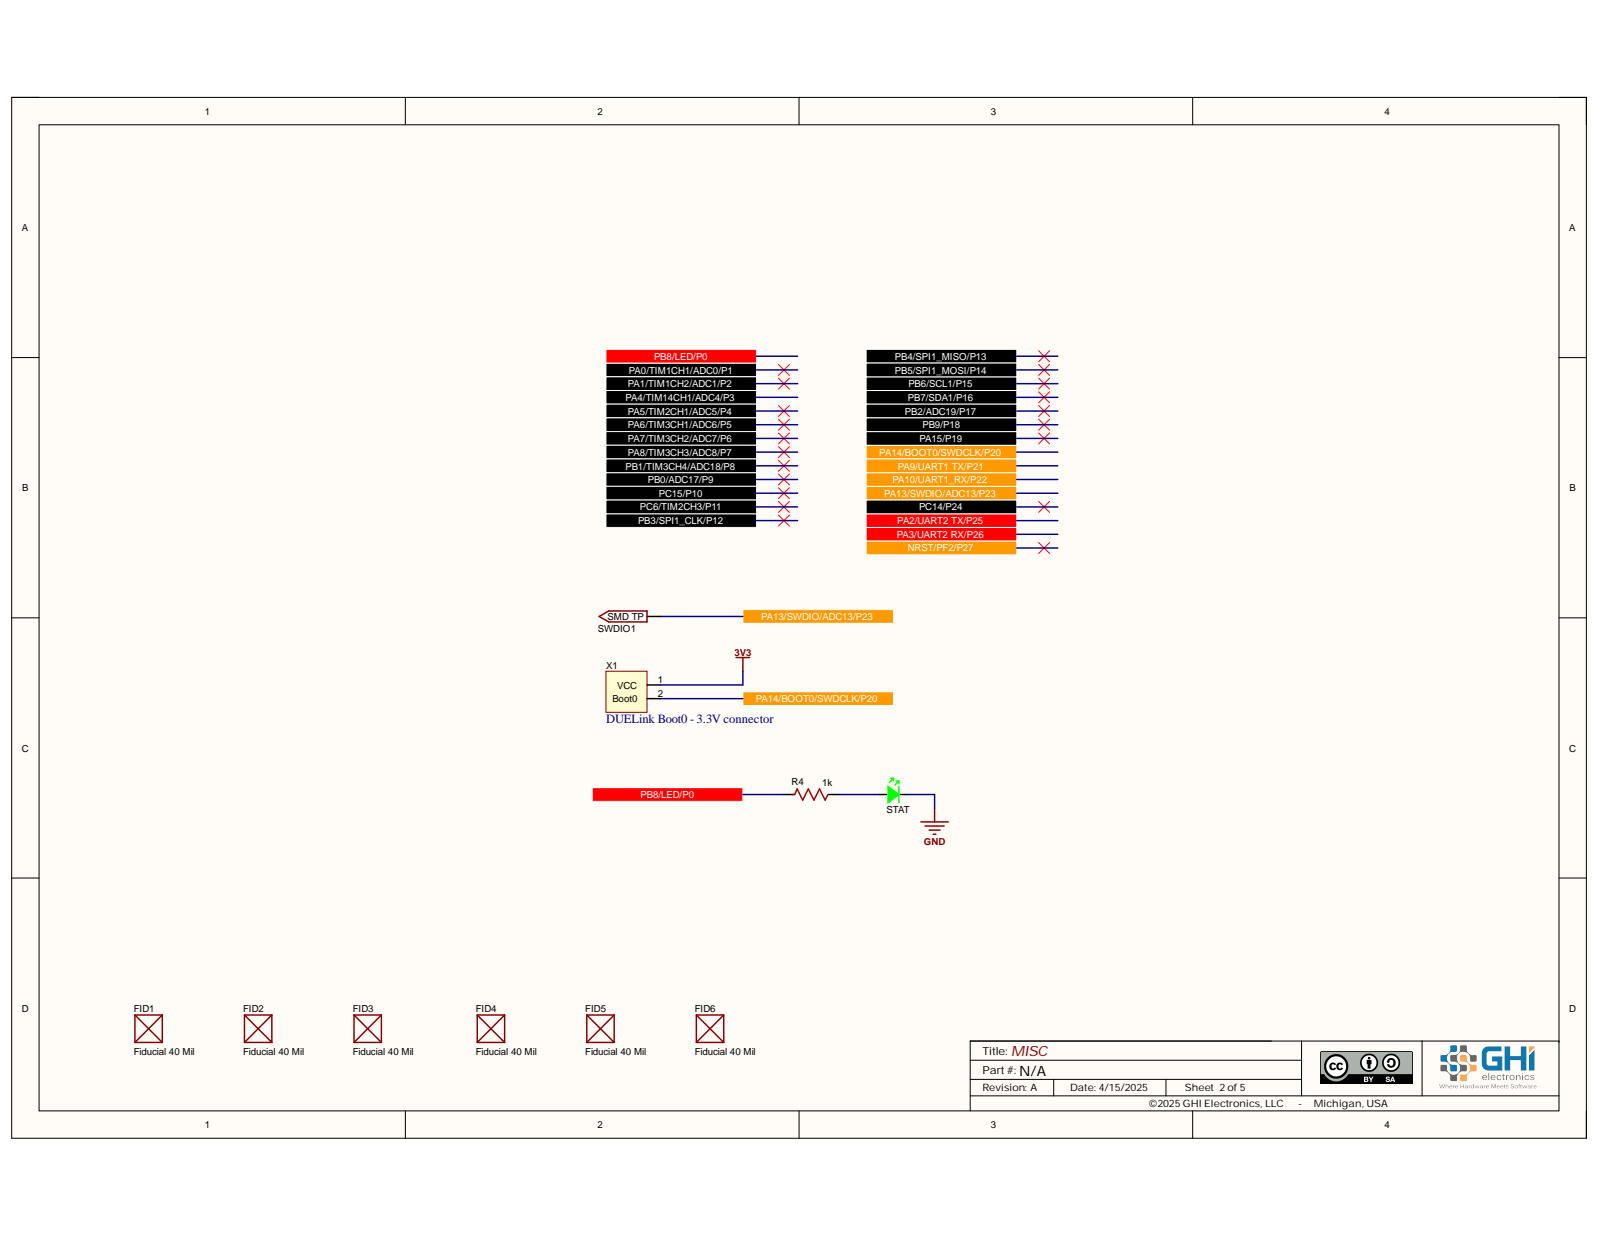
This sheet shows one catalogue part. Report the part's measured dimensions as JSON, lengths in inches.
{"part_name": "PCB; Board; J11; Conn_Molex_90120-0123_eec (+6 more)", "step_written_by": "Open CASCADE 7.5 (AUTOMOTIVE_DESIGN)", "units": "inches", "bodies": {"solids": 93, "faces": 1755, "planar": 1280, "cylindrical": 220, "other": 255}, "overall_size": [1.063, 0.866, 0.807], "volume_in3": 0.076, "surface_area_in2": 4.292, "round_holes": [[0.039, 5], [0.118, 4], [0.031, 2], [0.04, 2]], "round_bosses_or_shafts": [[0.63, 1], [0.394, 1], [0.343, 1], [0.026, 1]], "partial_cylinders_radius": [[0.005, 35], [0.006, 14], [0.02, 4], [0.138, 4], [0.007, 2], [0.007, 2], [0.007, 2]], "face_to_face_distances": [0.197, 0.205, 0.268, 0.26, 0.063, 0.039, 0.018, 0.015, 0.026, 0.02], "hole_center_spacings": [0.1, 0.094, 0.194, 0.258, 0.263, 0.341, 0.425, 0.43]}
